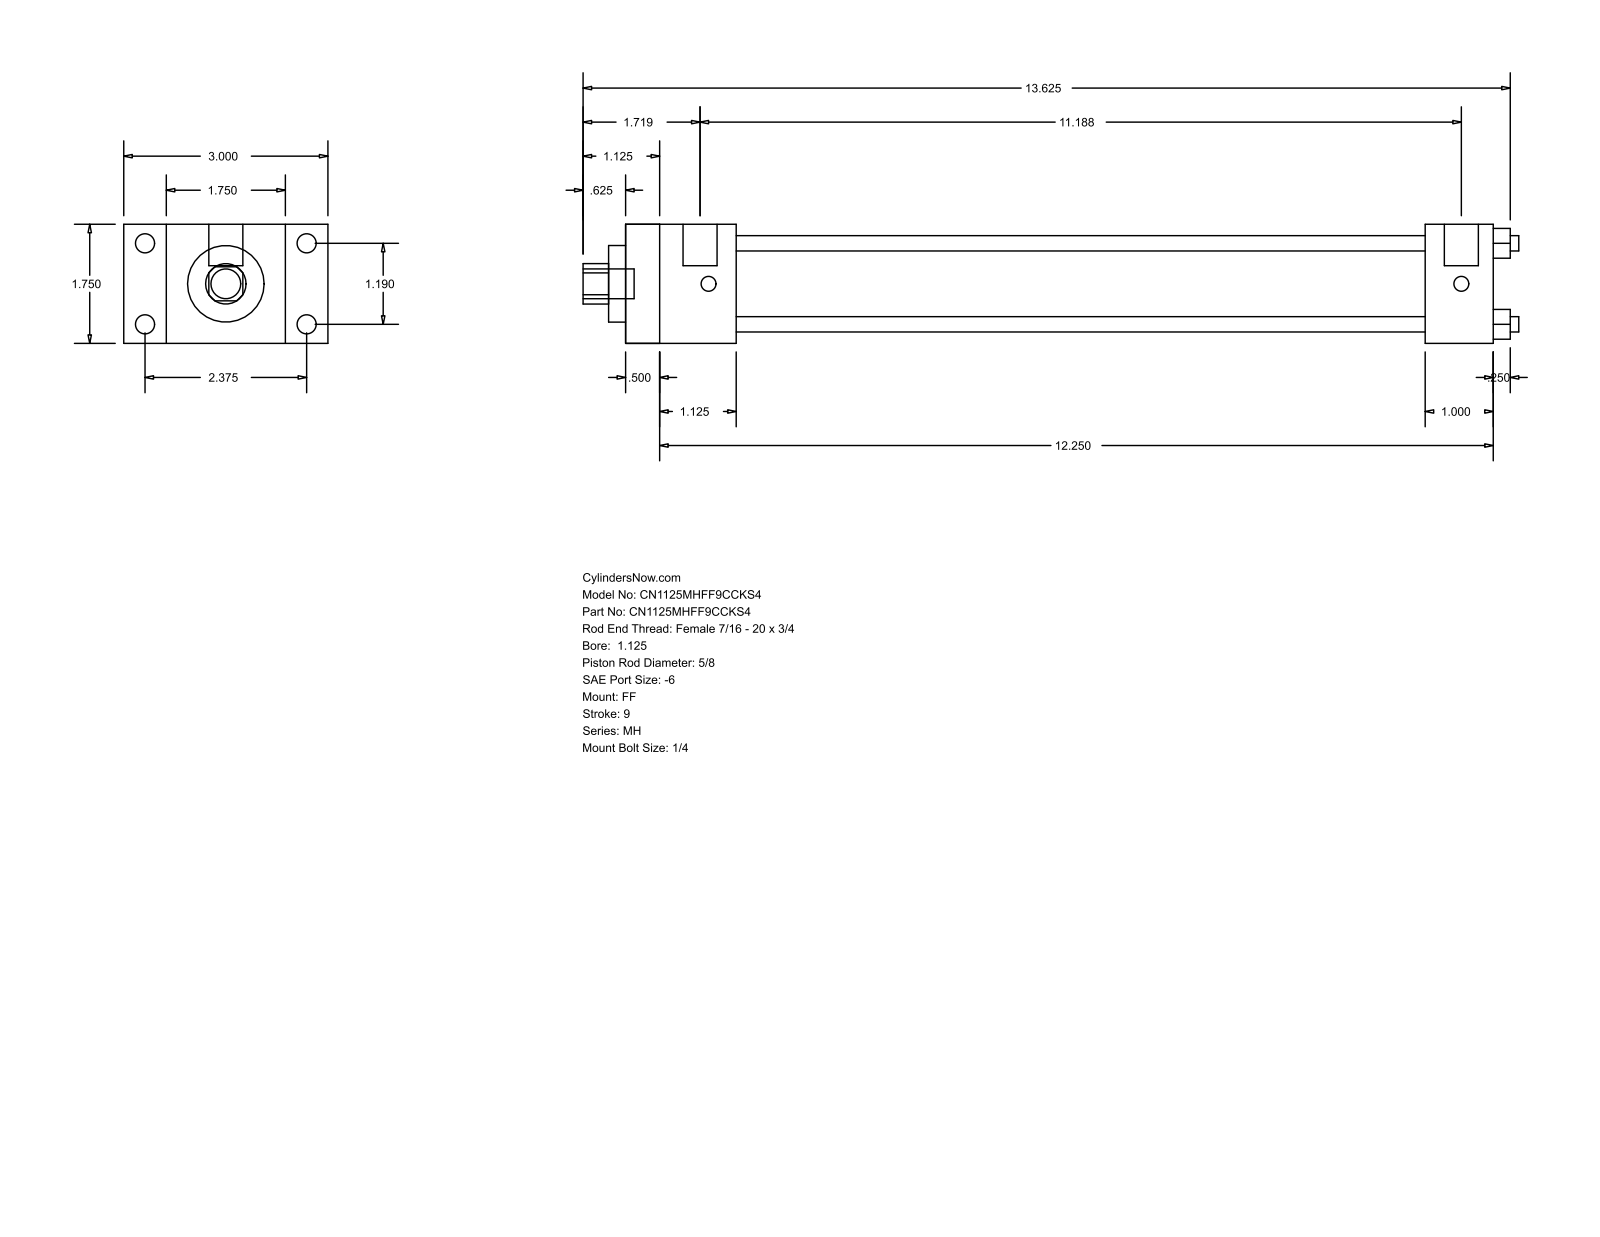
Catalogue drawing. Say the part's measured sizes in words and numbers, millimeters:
The part is named "MH_FF__0112_0.625". Its 3-D file was written by "GSSL Pune (CONFIG_CONTROL_DESIGN)". It is 0 solids with 92 faces: 64 planar, 28 cylindrical and 0 other. Overall it measures 349.25 by 76.2 by 44.45 millimeters. Round holes: 4 of diameter 5.71, 1 of diameter 15.88, 1 of diameter 28.57, 1 of diameter 34.92. Round bosses or shafts: 4 of diameter 7.14, 4 of diameter 5.56, 2 of diameter 12.7, 1 of diameter 11.11. Partial cylindrical surfaces (rounded edges, fillets, slot ends): 1 of radius 7.54. The main face-to-face distances are 44.46, 323.85, 12.69, 311.16, 15.87, 60.33, 28.58, 41.27, 298.44, 285.75. The hole center spacings are 21.37, 30.22, 42.74.
